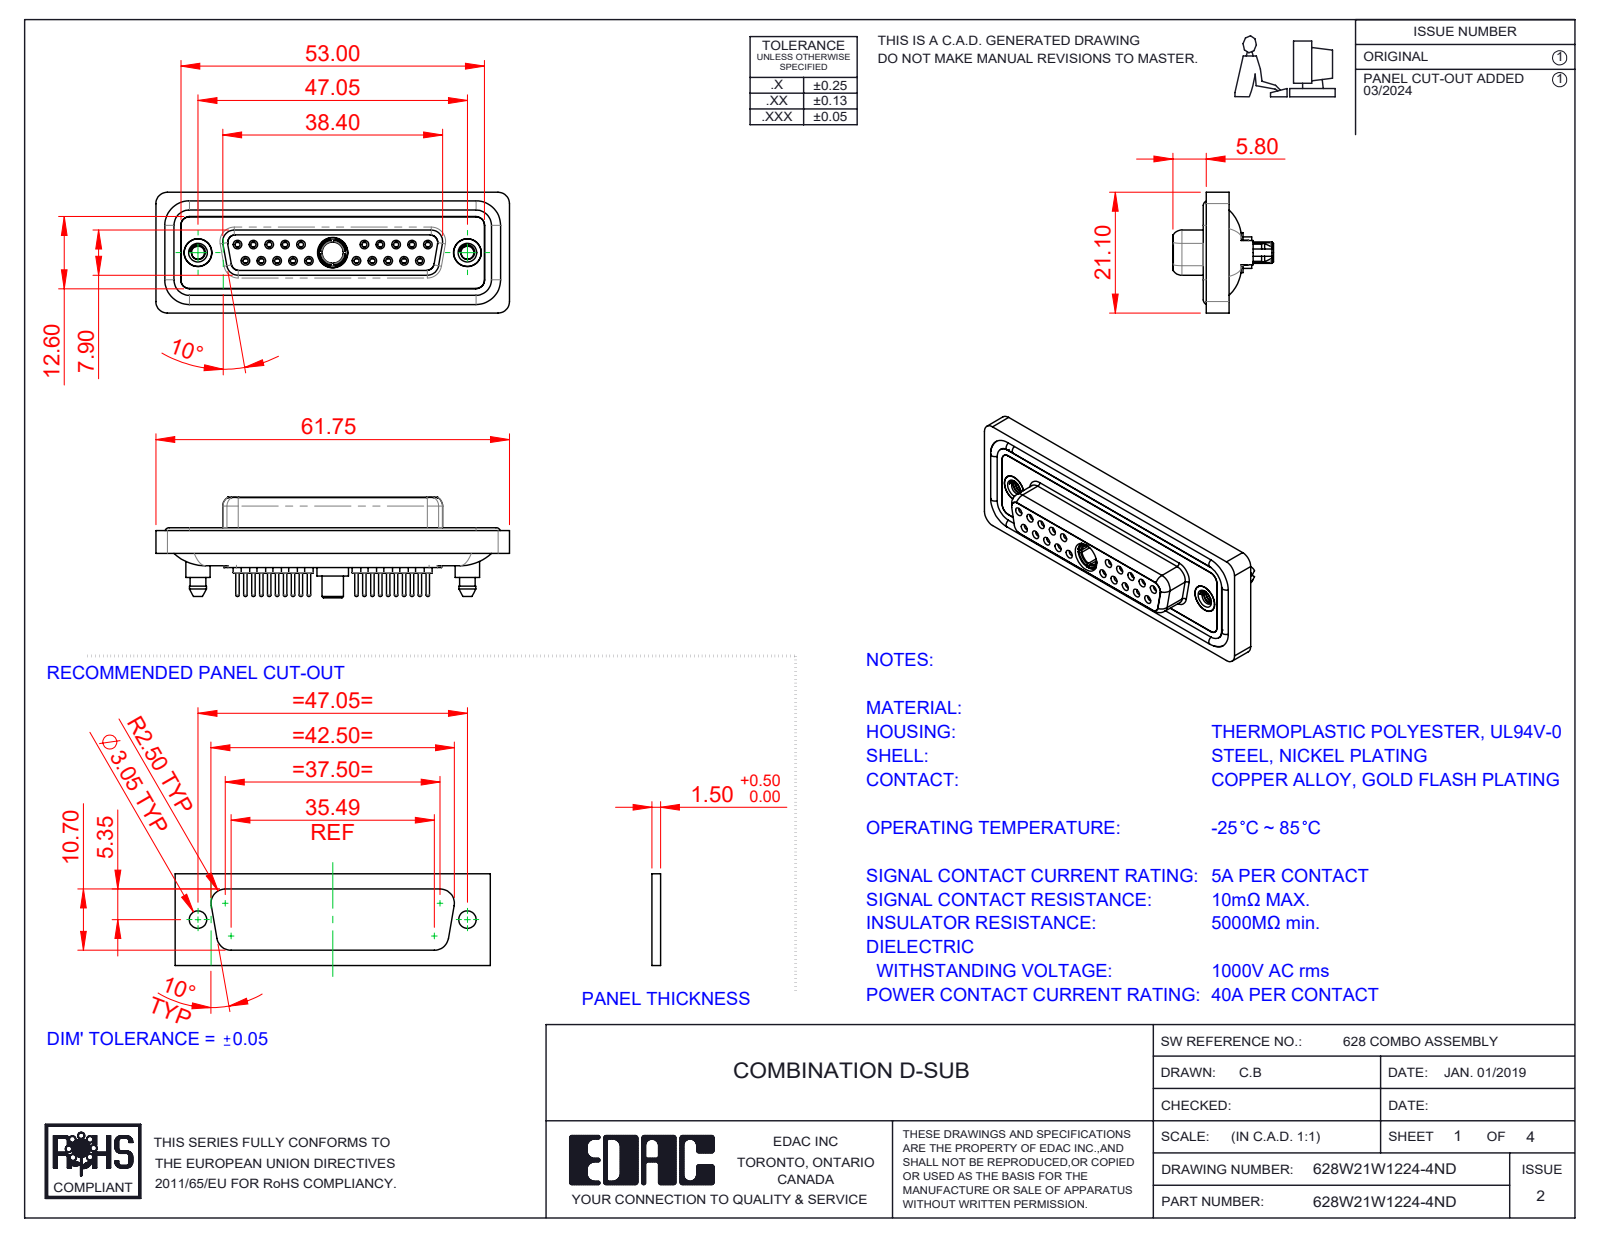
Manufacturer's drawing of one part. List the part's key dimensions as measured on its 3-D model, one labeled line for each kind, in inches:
Part name (STEP PRODUCT): 628W21W1224-4ND; 628Combo Housing_21W1; 628Combo Waterproof Housing_25 Contacts; 628Combo Contact Row 2_24 (+5 more)
STEP written by: SolidWorks 2023 (CONFIG_CONTROL_DESIGN)
Units: inches
Bodies: 29 solids, 1626 faces (450 planar, 639 cylindrical, 537 other)
Overall size (bounding box): 2.431 × 0.831 × 0.691
Volume: 0.52 in³ · Surface area: 22.25 in²
Round holes (diameter × count): ⌀0.035 ×20, ⌀0.043 ×20, ⌀0.059 ×20, ⌀0.079 ×20, ⌀0.063 ×10, ⌀0.067 ×10, ⌀0.191 ×3, ⌀0.089 ×2, ⌀0.157 ×2, ⌀0.159 ×2, ⌀0.197 ×2, ⌀0.146 ×1
Round bosses / shafts (diameter × count): ⌀0.087 ×20, ⌀0.024 ×20, ⌀0.063 ×14, ⌀0.213 ×2, ⌀0.195 ×2, ⌀0.189 ×2, ⌀0.167 ×2, ⌀0.217 ×1
Partial cylindrical surfaces — rounded edges, fillets, slot ends (radius × count): R0.059 ×24, R0.079 ×18, R0.063 ×10, R0.053 ×8, R0.01 ×4, R0.02 ×4, R0.024 ×4, R0.026 ×4
Main face-to-face distances: 0.016, 0.071, 0.293, 0.26, 0.222, 0.063, 0.02, 0.278, 0.114, 0.043
Hole centre spacings: 0.124, 0.109, 0.218, 0.198, 0.327, 0.294, 0.654, 0.763
